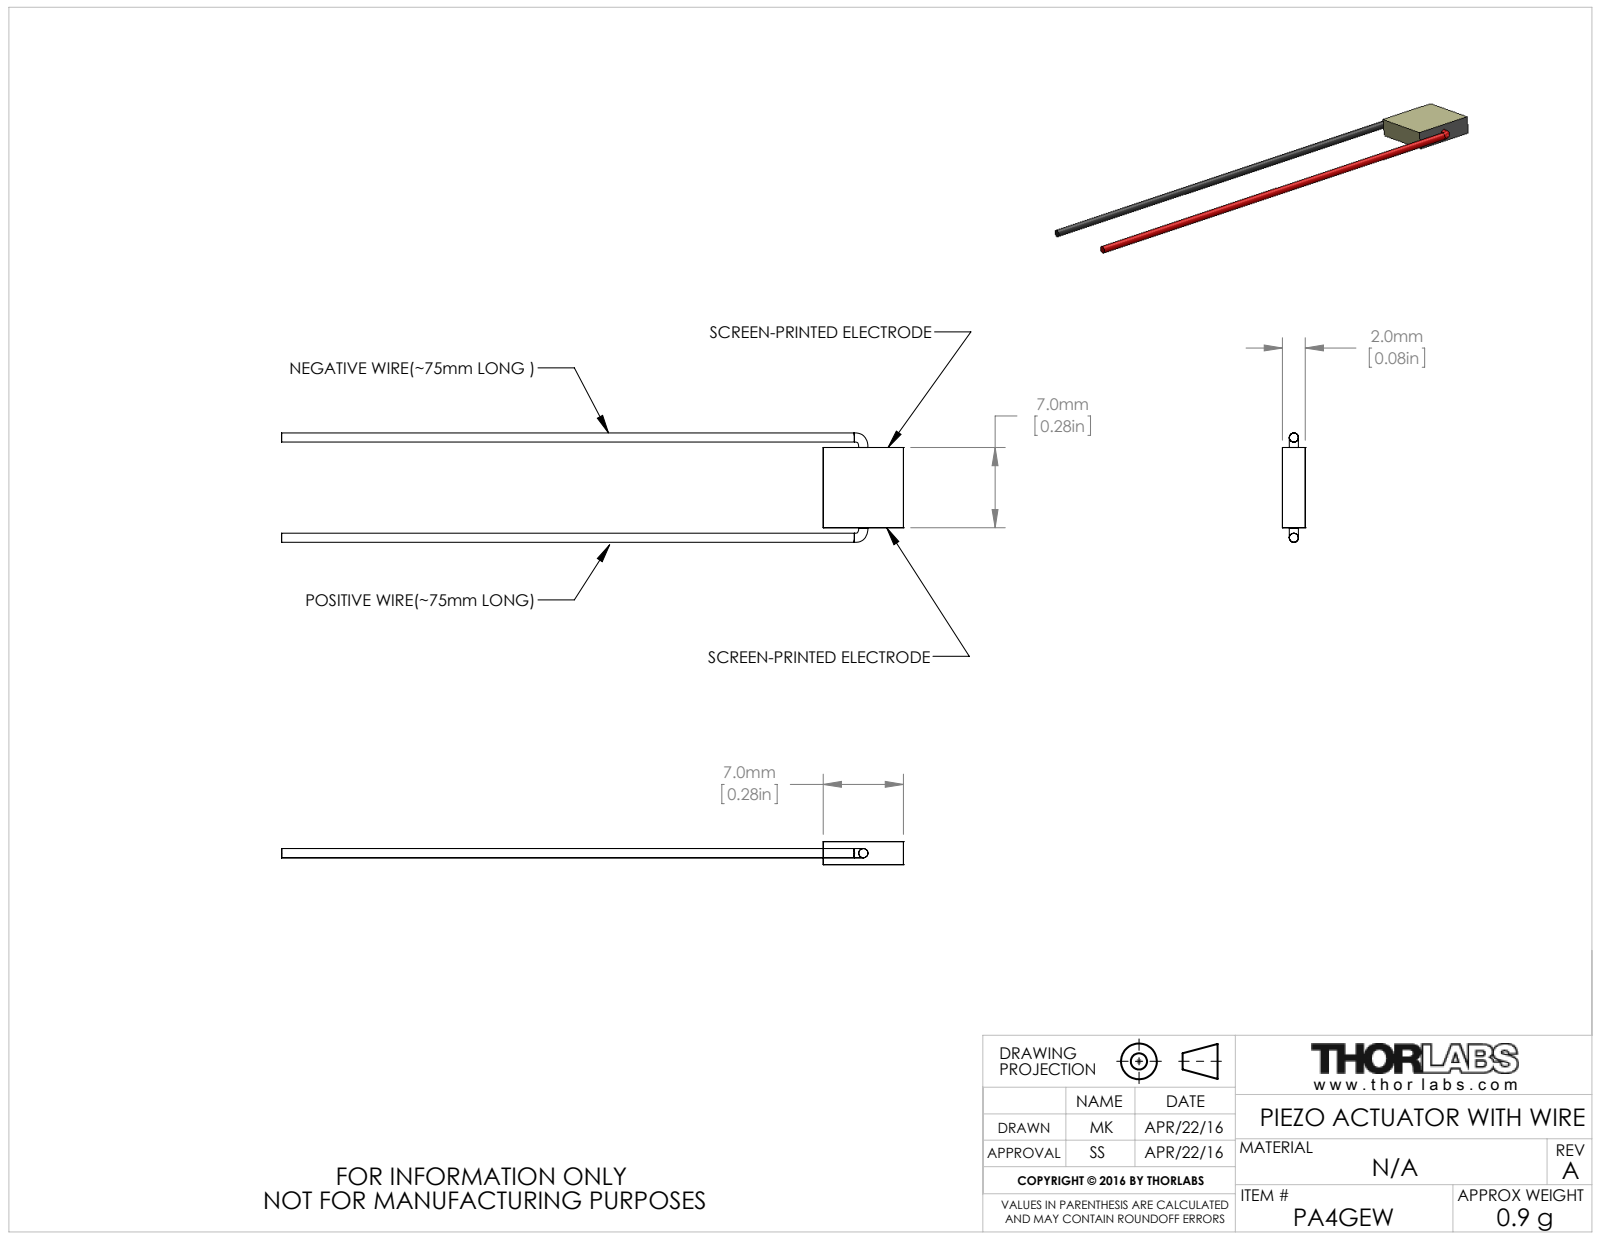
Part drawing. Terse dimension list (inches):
name: CTN002590
written by: SolidWorks 2014 (AUTOMOTIVE_DESIGN)
unit: in
bodies: 3 solids, 18 faces (10 planar, 0 cylindrical, 8 other)
size: 2.137 × 0.376 × 0.079
volume: 0.009 in³; area: 0.642 in²
face distances: 0.079, 0.276, 2.137, 1.862
